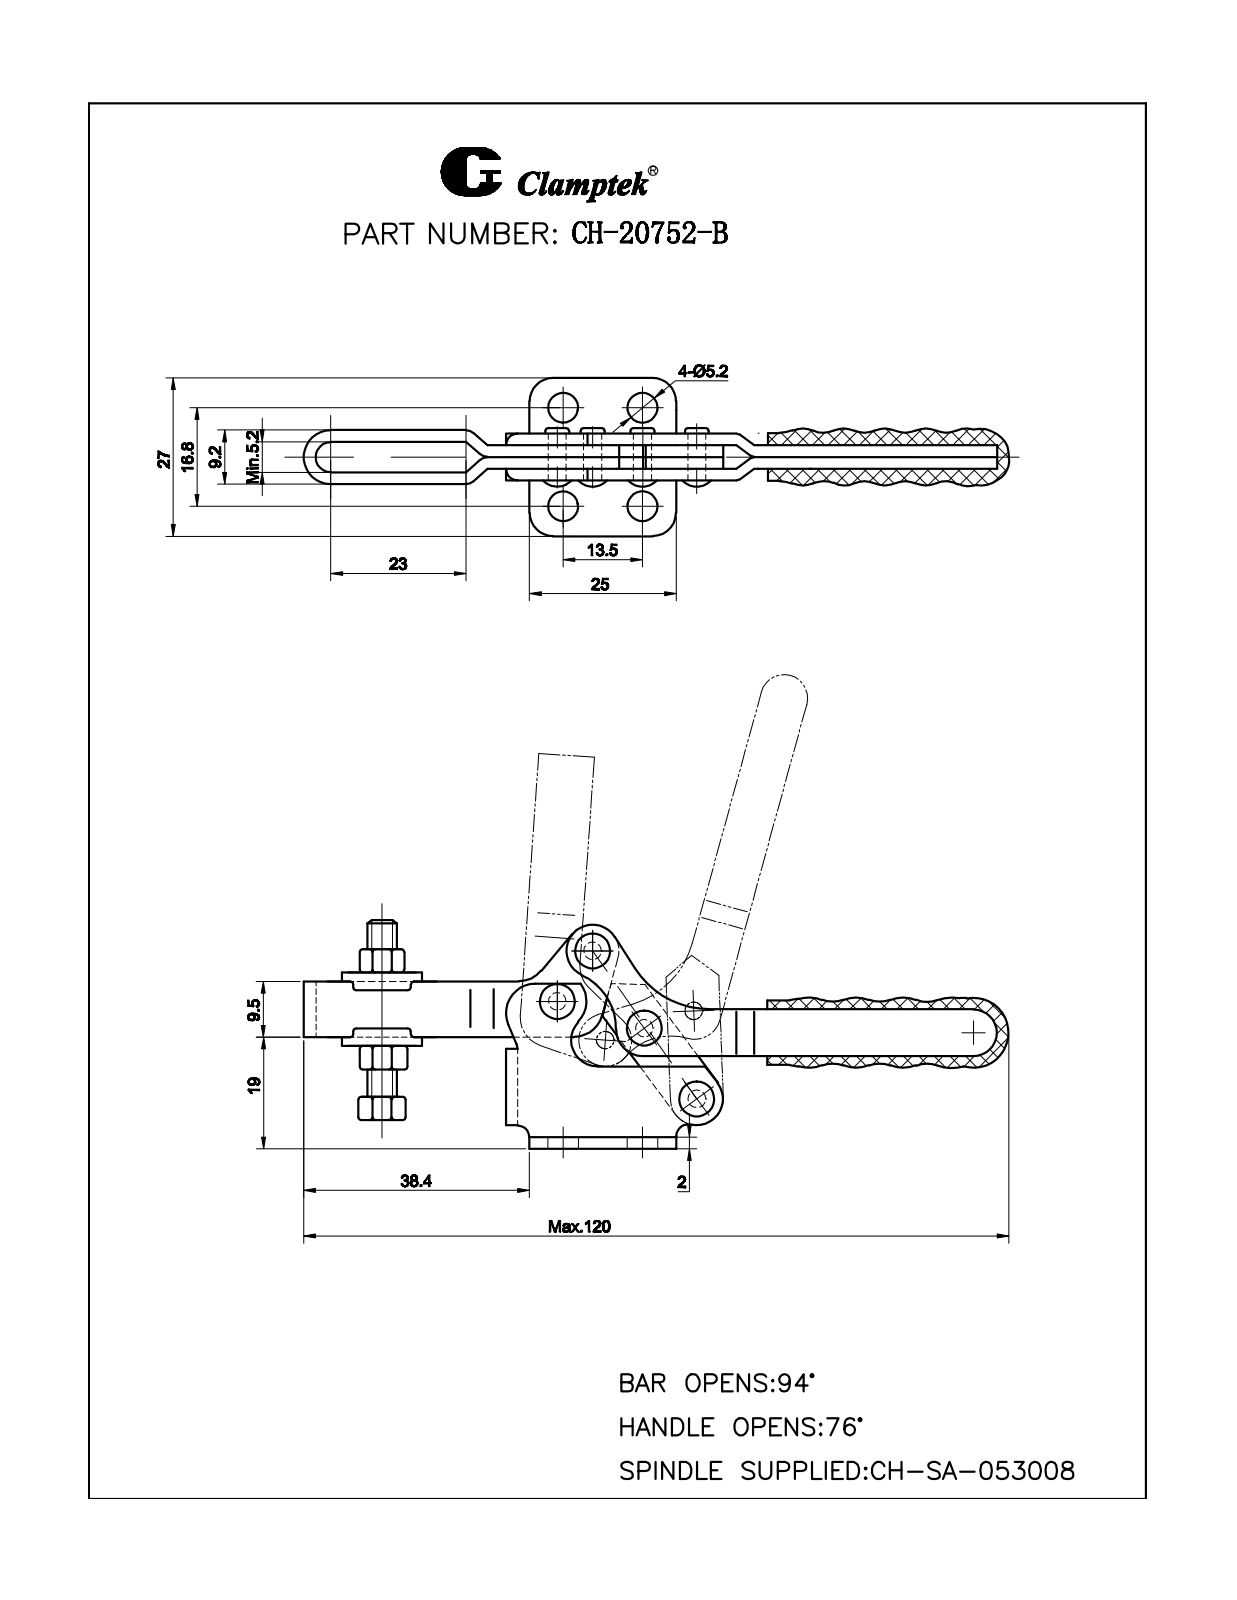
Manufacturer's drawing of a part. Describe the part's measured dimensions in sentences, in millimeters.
The part is named "??_??; FW140_??; 20752-B-05_??; CH-20752-B (+6 more)". Its 3-D file was written by "SolidWorks 2005179 (CONFIG_CONTROL_DESIGN)". It is 17 solids with 812 faces: 297 planar, 231 cylindrical and 284 other. Overall it measures 120.11 by 38.2 by 27 millimeters. Its volume is 16 177 cubic millimeters and its surface area 17 610 square millimeters. Round holes: 4 of diameter 2.4, 4 of diameter 3, 4 of diameter 5.2, 1 of diameter 1.2, 1 of diameter 4.2, 1 of diameter 6.8. Round bosses or shafts: 1 of diameter 5, 1 of diameter 1.03. Partial cylindrical surfaces (rounded edges, fillets, slot ends): 14 of radius 2, 5 of radius 5, 4 of radius 1.5, 4 of radius 4.5, 3 of radius 4, 2 of radius 1, 2 of radius 2, 1 of radius 3. The main face-to-face distances are 2, 4, 6, 8, 1, 3, 5, 7, 9, 1.5. The hole center spacings are 13.5, 16.8, 21.55, 10.48, 15, 15.46, 15.85, 28.98.
